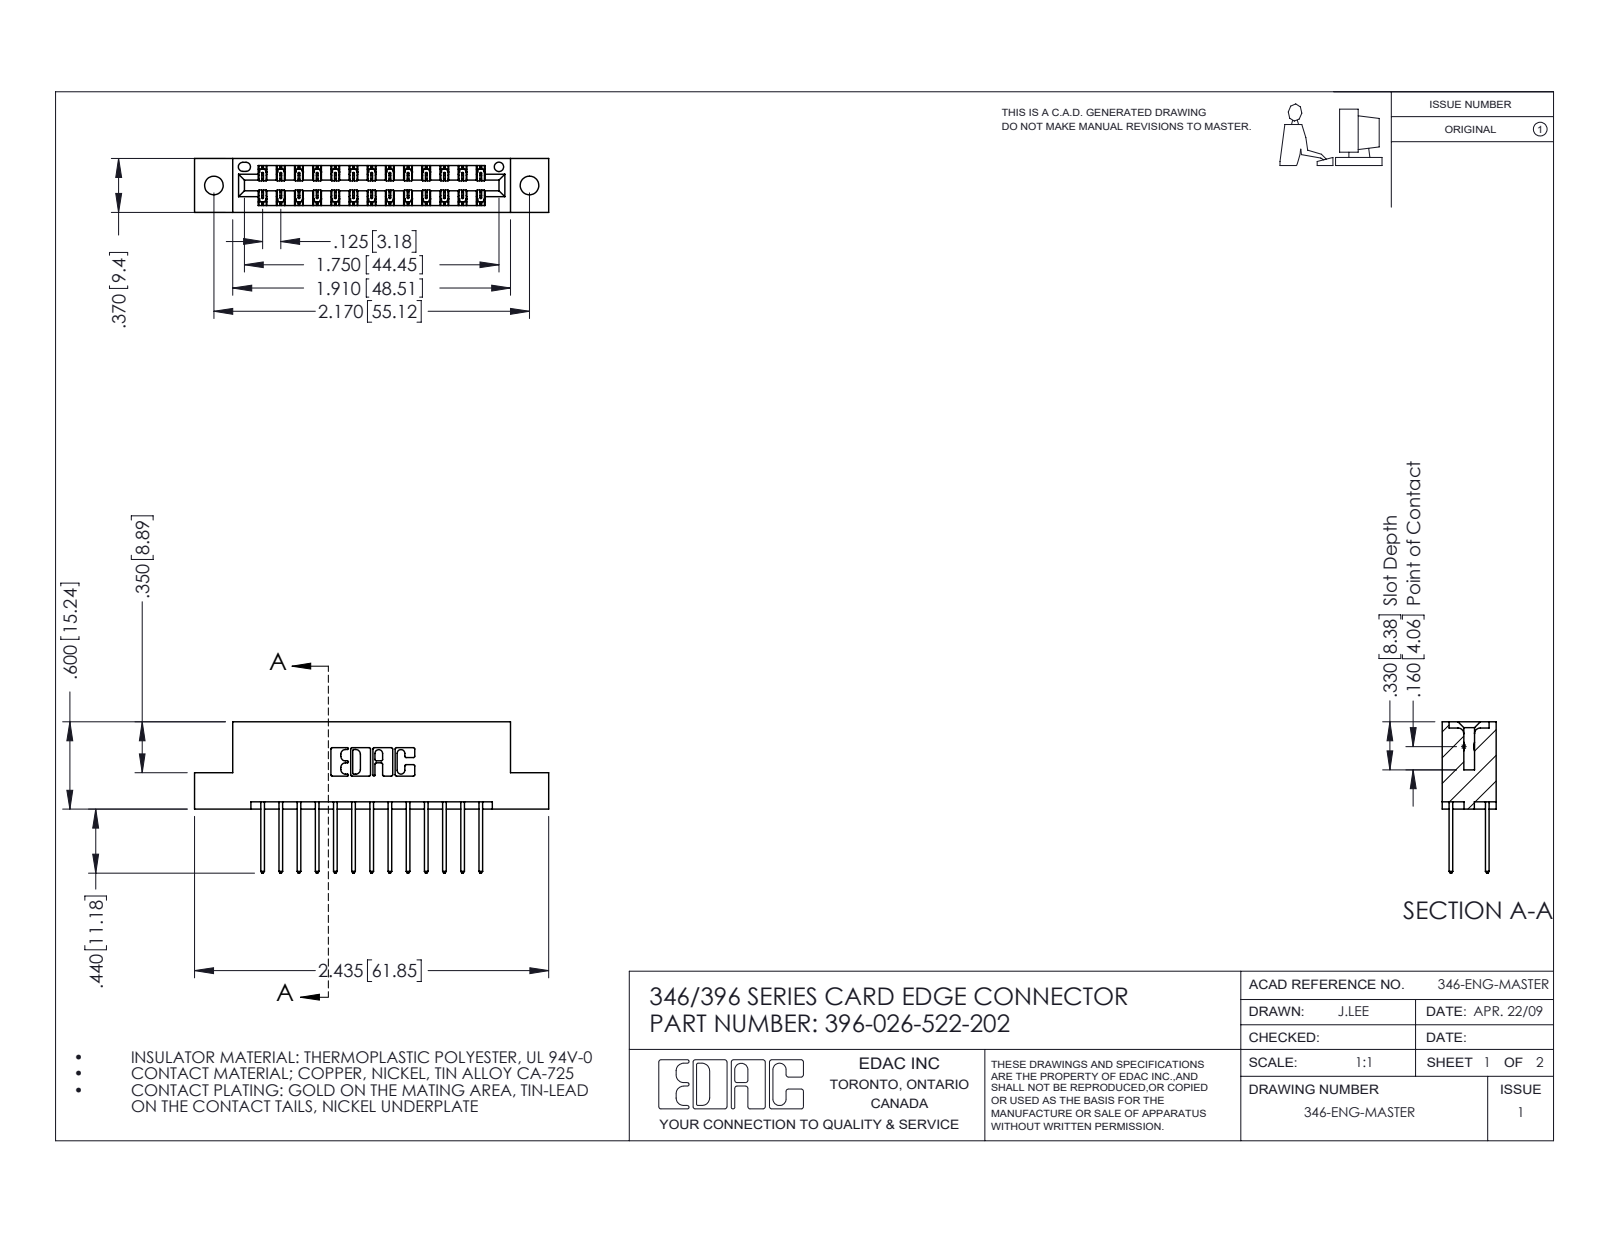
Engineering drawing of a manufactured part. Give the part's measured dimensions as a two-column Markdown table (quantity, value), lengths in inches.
| quantity | value |
| --- | --- |
| part name | 396-026-522-202; 345-292-001_345-293-122; 346 Part_Flush Mounting Lugs - 0.128 Dia |
| STEP written by | SolidWorks 2016 (CONFIG_CONTROL_DESIGN) |
| units | inches |
| bodies | 27 solids, 1474 faces (986 planar, 488 cylindrical, 0 other) |
| overall size | 2.435 × 1.04 × 0.37 |
| volume | 0.356 in³ |
| surface area | 11.79 in² |
| round holes (diameter × count) | 0.128 × 2, 0.064 × 1 |
| partial cylindrical surfaces (radius × count) | 0.006 × 39, 0.01 × 26, 0.01 × 22, 0.007 × 6, 0.031 × 6, 0.026 × 3, 0.014 × 2, 0.022 × 2 |
| main face-to-face distances | 0.25, 0.048, 0.322, 0.37, 0.072, 0.298, 0.025, 0.275, 0.148, 0.222 |
| hole center spacings | 0.246, 1.964, 2.17 |
